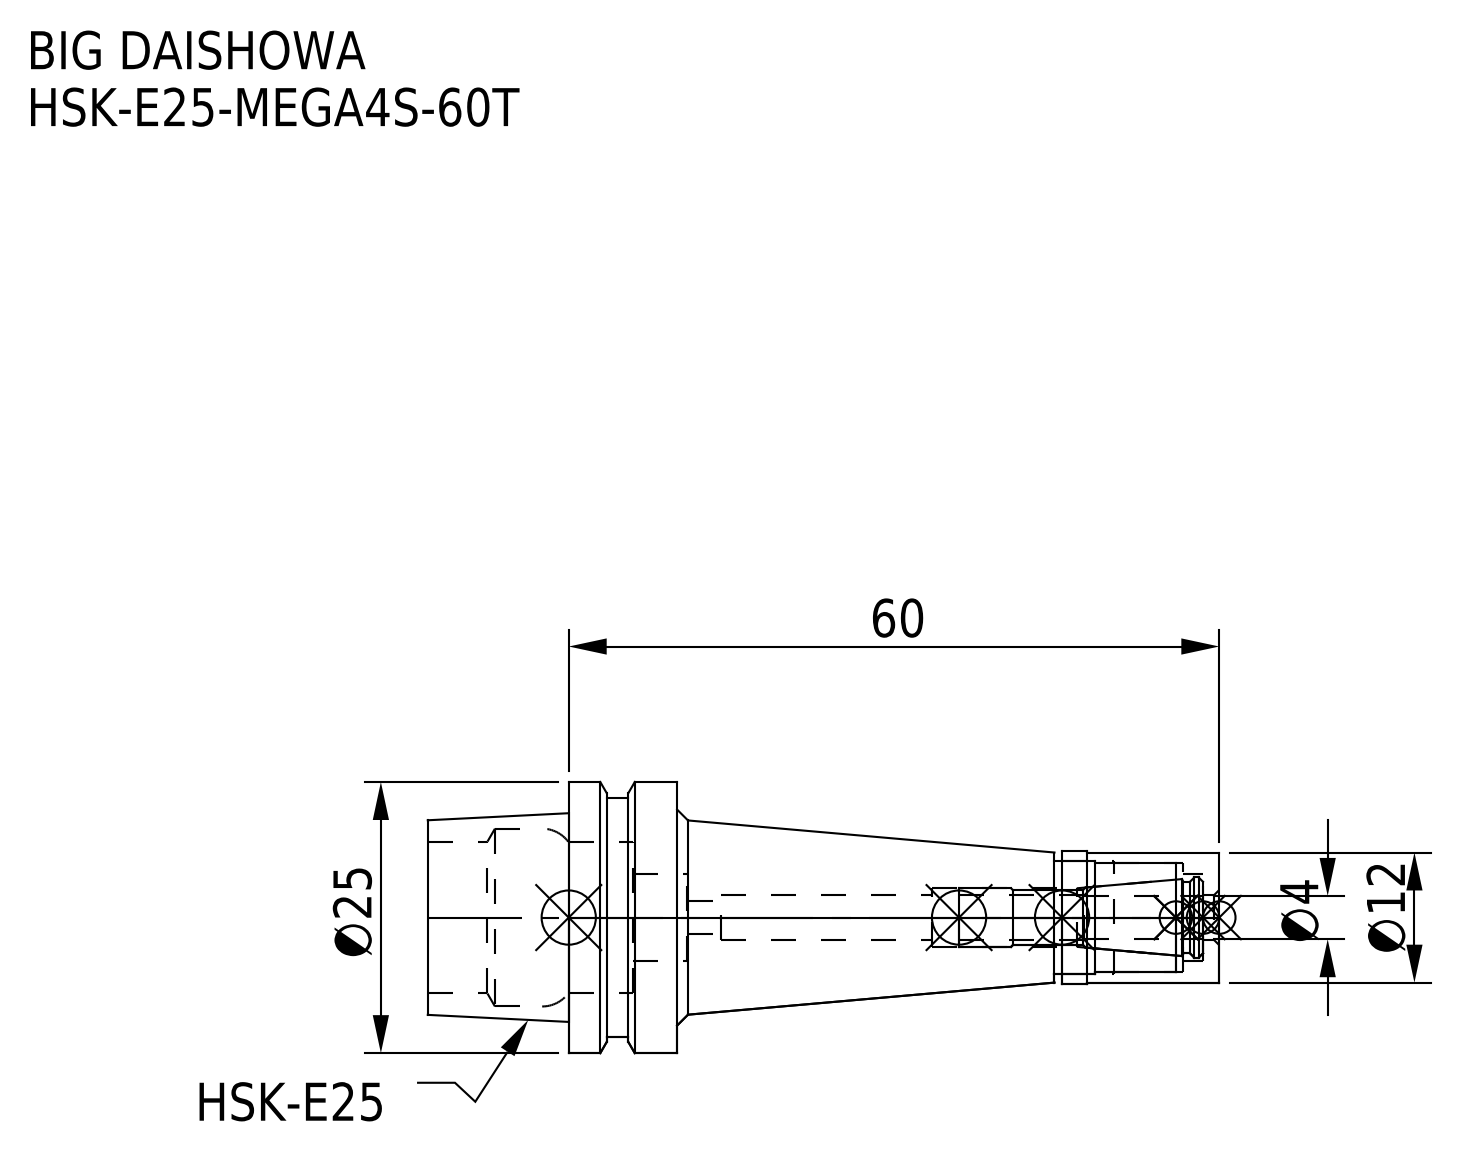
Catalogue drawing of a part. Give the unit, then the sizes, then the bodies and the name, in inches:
Units: inches
Overall size (bounding box): 2.874 × 0.984 × 0.984
Round holes (diameter × count): ⌀0.118 ×1, ⌀0.161 ×1, ⌀0.165 ×1, ⌀0.213 ×1, ⌀0.315 ×1, ⌀0.394 ×1, ⌀0.413 ×1, ⌀0.551 ×1, ⌀0.646 ×1
Round bosses / shafts (diameter × count): ⌀0.984 ×1, ⌀0.866 ×1, ⌀0.484 ×1, ⌀0.472 ×1
Main face-to-face distances: 0.394, 0.512, 0.159, 0.234, 0.906, 0.746, 1.969, 2.128, 2.362, 2.874
Volume: 0.708 in³ · Surface area: 11.41 in²
Bodies: 2 solids, 74 faces (18 planar, 38 cylindrical, 18 other)
Part name (STEP PRODUCT): HSK-E25-MEGA4S-60T_1.stp; HSK-E25-MEGA4S-60T-040.stp; HSK-E25-MEGA4S-60T-040-FreeParts; HSK-E25-MEGA4S-60T (+3 more)
STEP written by: SolidWorks 2019 (CONFIG_CONTROL_DESIGN)
